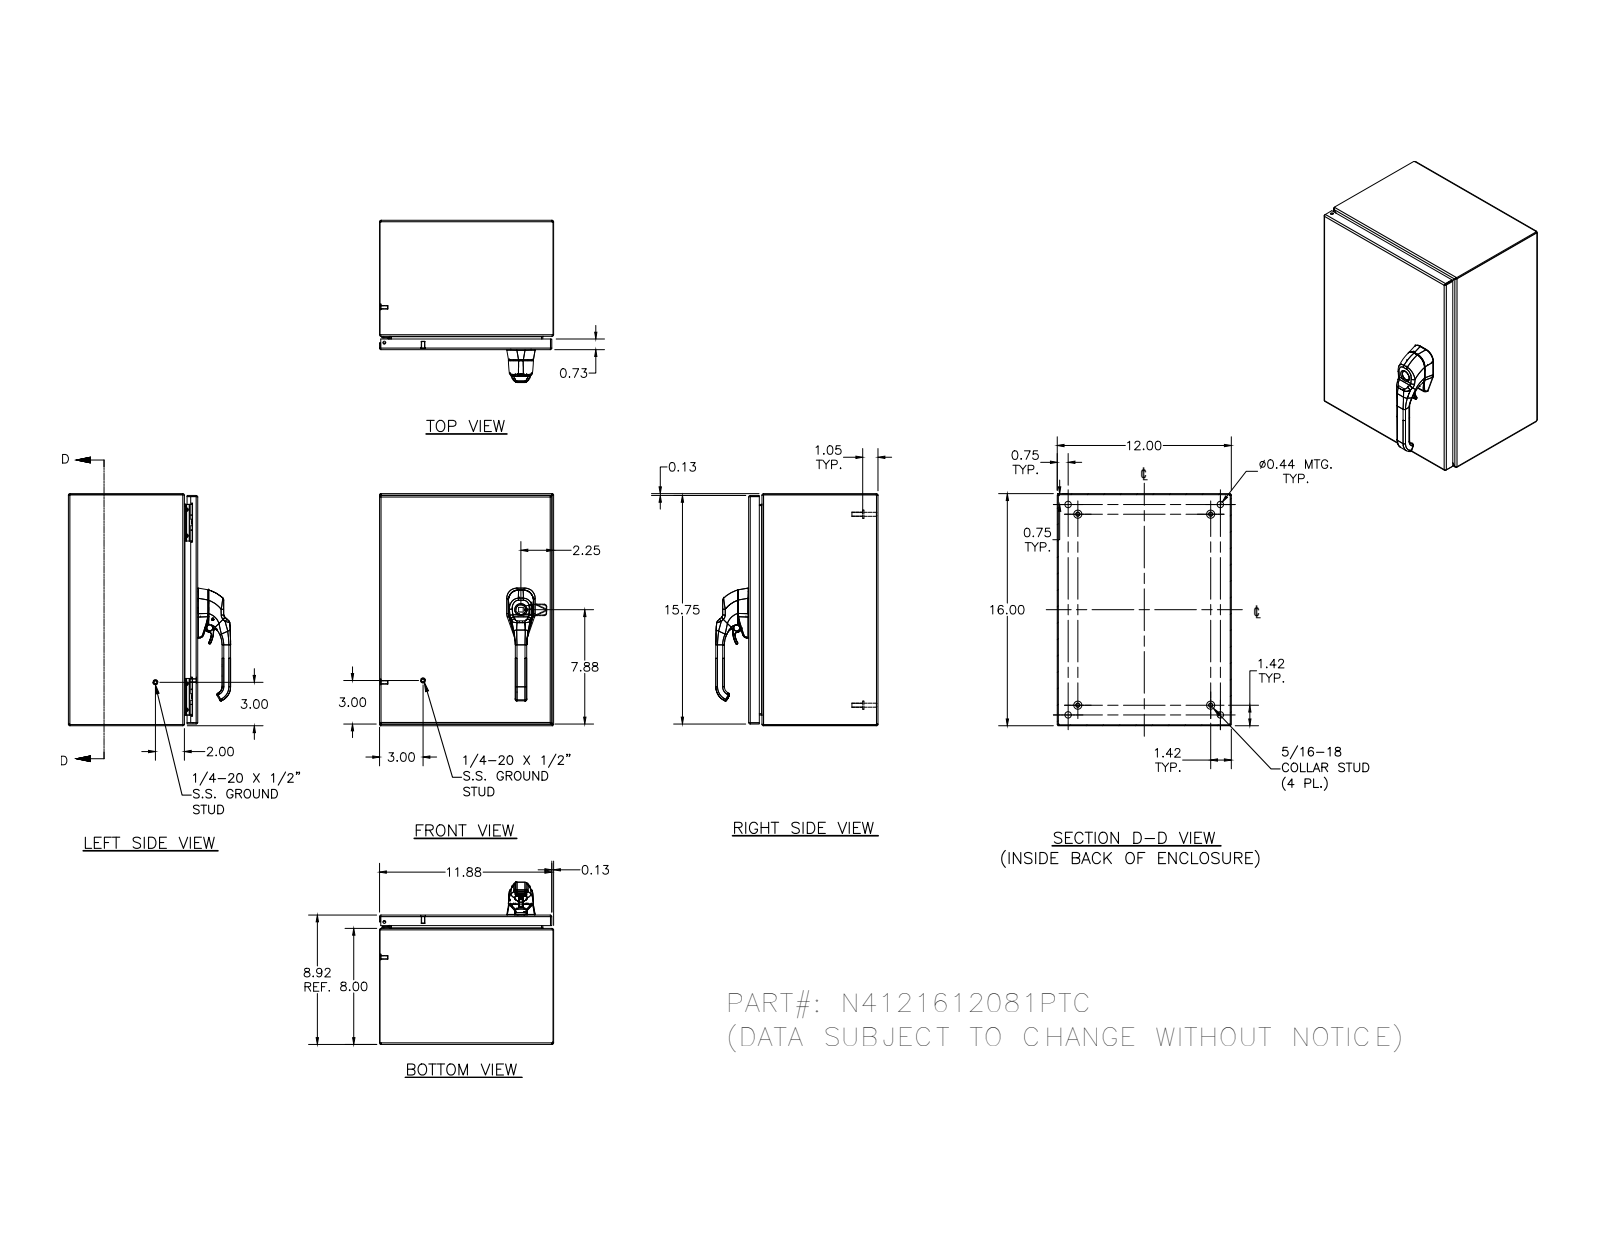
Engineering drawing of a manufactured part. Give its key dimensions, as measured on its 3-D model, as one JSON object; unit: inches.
{"part_name": "N4121612081PTC", "step_written_by": "SolidWorks 2018 (AUTOMOTIVE_DESIGN)", "units": "inches", "bodies": {"solids": 28, "faces": 1280, "planar": 417, "cylindrical": 474, "other": 389}, "overall_size": [16, 12, 11.095], "volume_in3": 79.86, "surface_area_in2": 1950, "round_holes": [[0.188, 5], [0.093, 4], [0.152, 4], [0.167, 4], [0.172, 4], [0.437, 4], [0.28, 3], [0.156, 2], [0.187, 1]], "round_bosses_or_shafts": [[0.25, 10], [0.563, 4], [0.36, 4], [0.32, 4], [0.3, 4], [0.275, 4], [0.256, 4], [0.164, 4]], "partial_cylinders_radius": [[0.031, 30], [0.05, 26], [0.105, 20], [0.016, 18], [0.125, 14], [0.032, 8], [0.067, 8], [0.068, 8]], "face_to_face_distances": [0.074, 8.843, 11.926, 15.926, 8.917, 8.769, 12, 11.852, 16, 15.852], "hole_center_spacings": [11.996, 0.017, 0.66, 12.656, 0.019, 0.5, 0.648, 0.656]}
